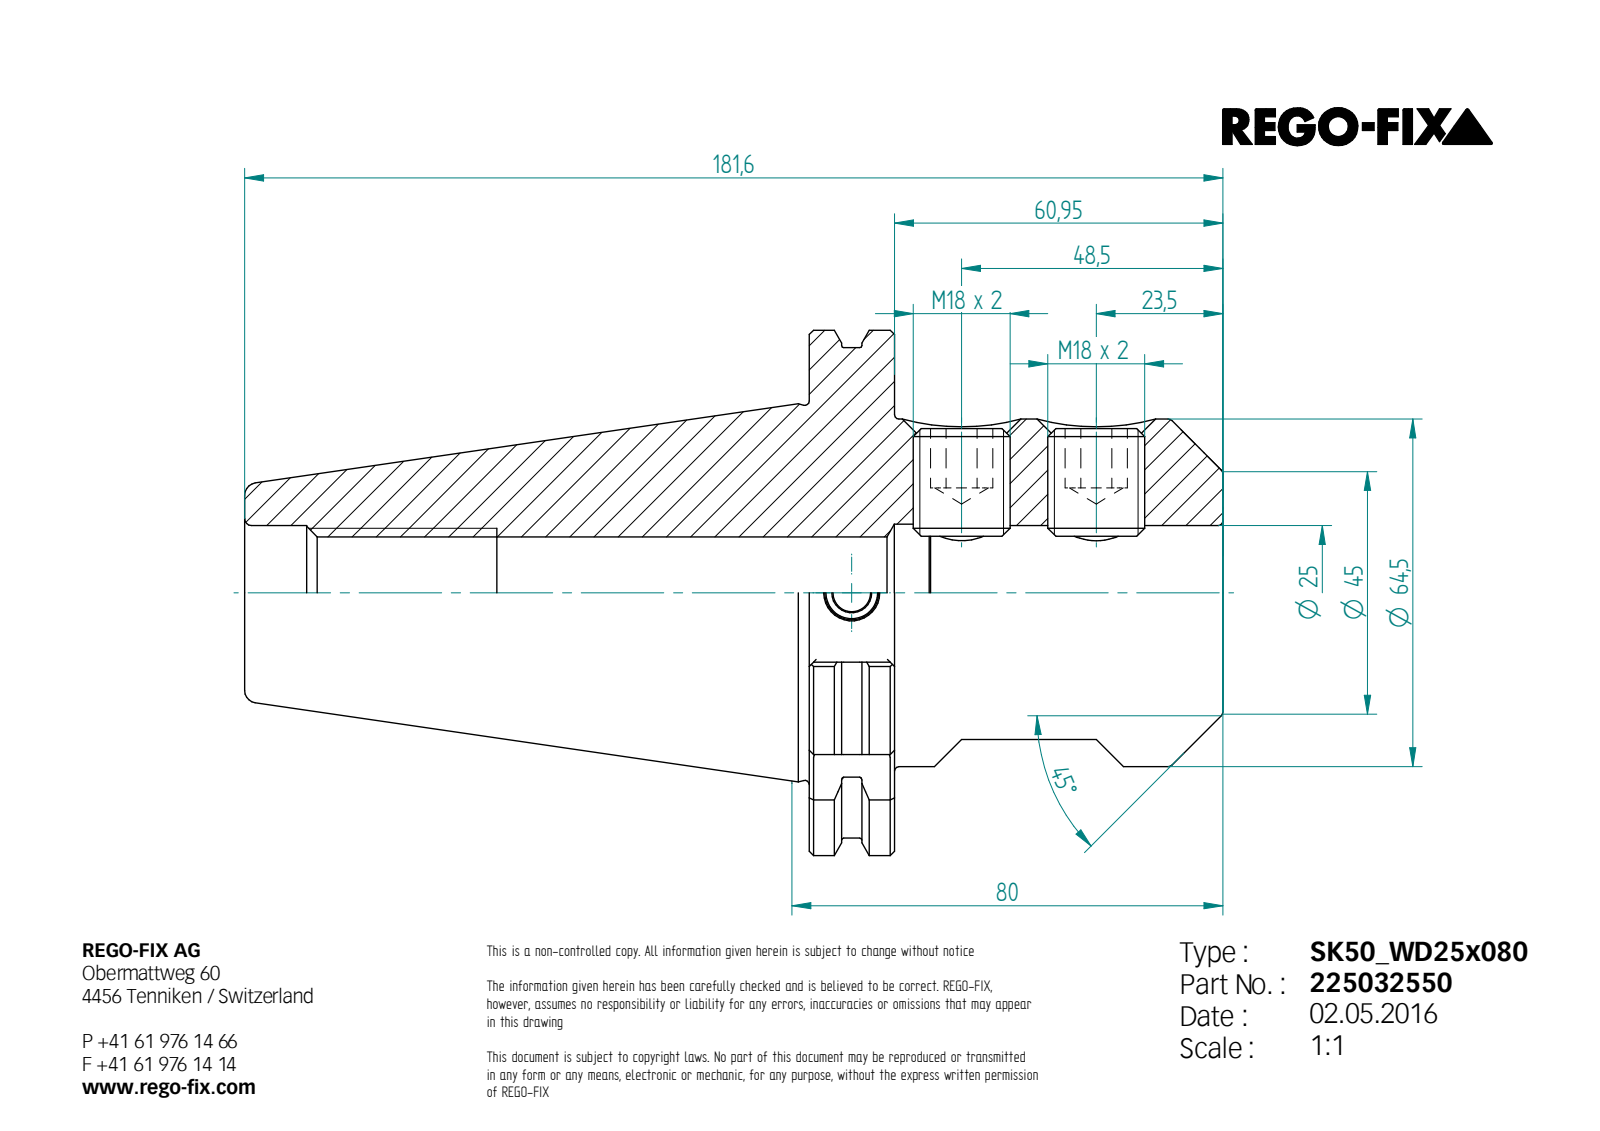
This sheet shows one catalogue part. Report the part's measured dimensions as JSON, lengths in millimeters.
{"step_written_by": "Unknown (AUTOMOTIVE_DESIGN)", "units": "millimeters", "bodies": {"solids": 3, "faces": 141, "planar": 72, "cylindrical": 26, "other": 43}, "overall_size": [181.6, 97.5, 93.58], "volume_mm3": 477150, "surface_area_mm2": 63692, "round_holes": [[15.84, 2], [7, 1], [10, 1], [20.75, 1], [25, 1], [25.5, 1]], "round_bosses_or_shafts": [[18, 2], [91, 1], [64.5, 1]], "partial_cylinders_radius": [[0.5, 5], [48.75, 1]], "face_to_face_distances": [15.85, 76.8, 60.95, 104.8, 120.65, 181.6, 10, 37.7, 72.8, 21.65], "hole_center_spacings": [25]}
